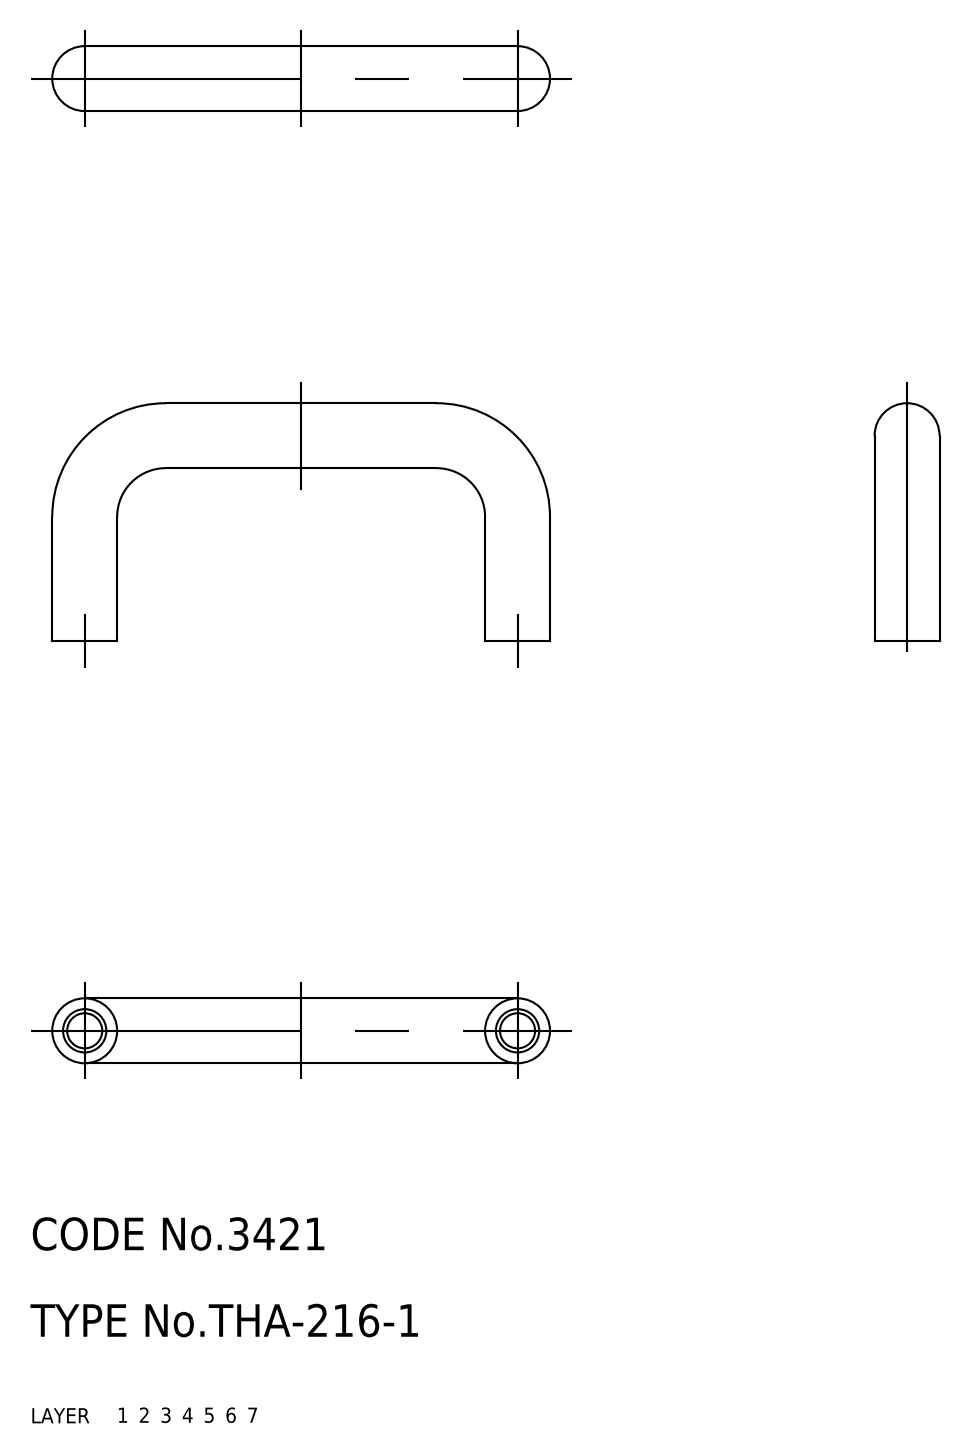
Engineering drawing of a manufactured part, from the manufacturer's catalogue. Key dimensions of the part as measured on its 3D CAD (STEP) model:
Part name (STEP PRODUCT): pull
STEP written by: CADfix (AUTOMOTIVE_DESIGN)
Units: millimetres
Bodies: 1 solid, 18 faces (0 planar, 0 cylindrical, 18 other)
Overall size (bounding box): 46 × 22 × 6
Volume: 1 830 mm³ · Surface area: 1 608 mm²
